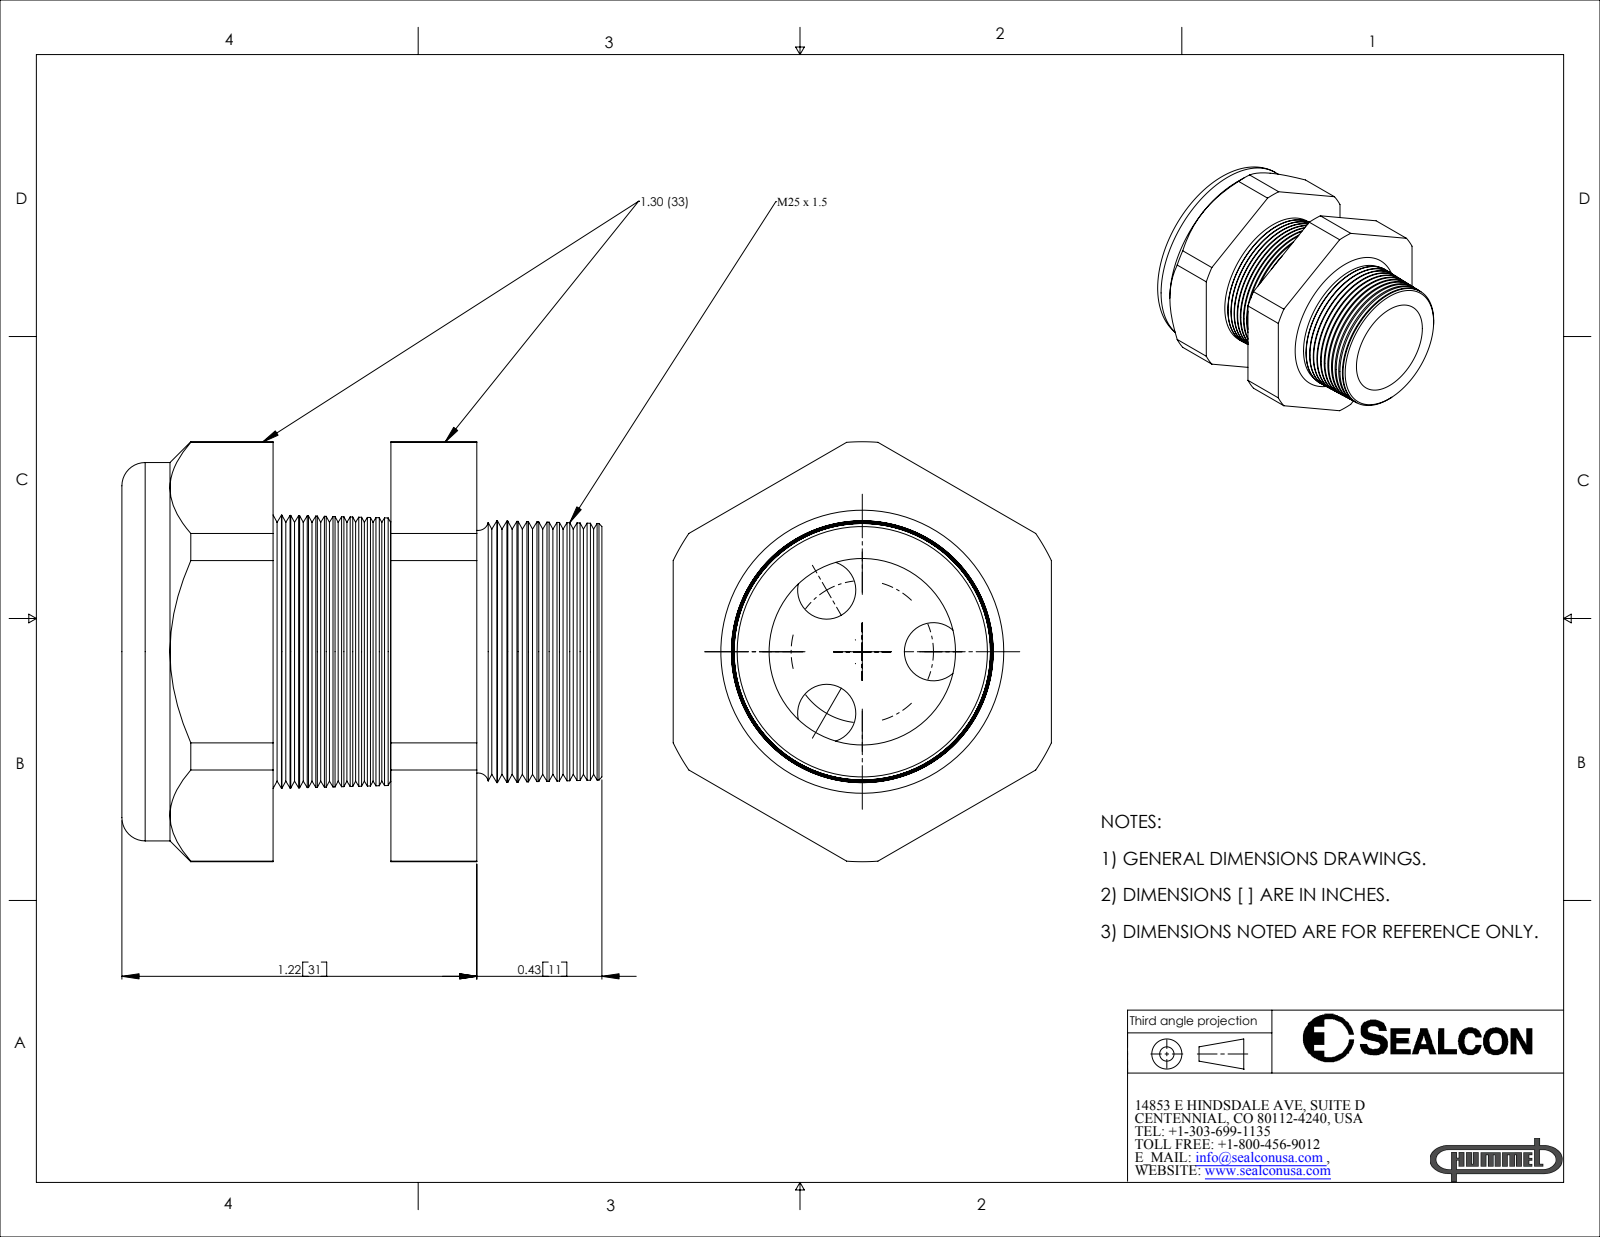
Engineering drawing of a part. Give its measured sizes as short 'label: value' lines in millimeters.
name: CD25M7-BK
written by: SolidWorks 2007 (CONFIG_CONTROL_DESIGN)
unit: mm
bodies: 2 solids, 212 faces (20 planar, 26 cylindrical, 166 other)
size: 41.9 × 36.7 × 33
volume: 19 010 mm³; area: 10 960 mm²
holes: 3× ⌀5.1, 1× ⌀17.5, 1× ⌀18
bosses: 1× ⌀33
rounds: 1× R18.3
face distances: 33, 10.3, 17.8, 7.5, 13.2, 23.5, 31, 8.9, 4.3, 14.6
hole spacings: 6.2, 10.8
